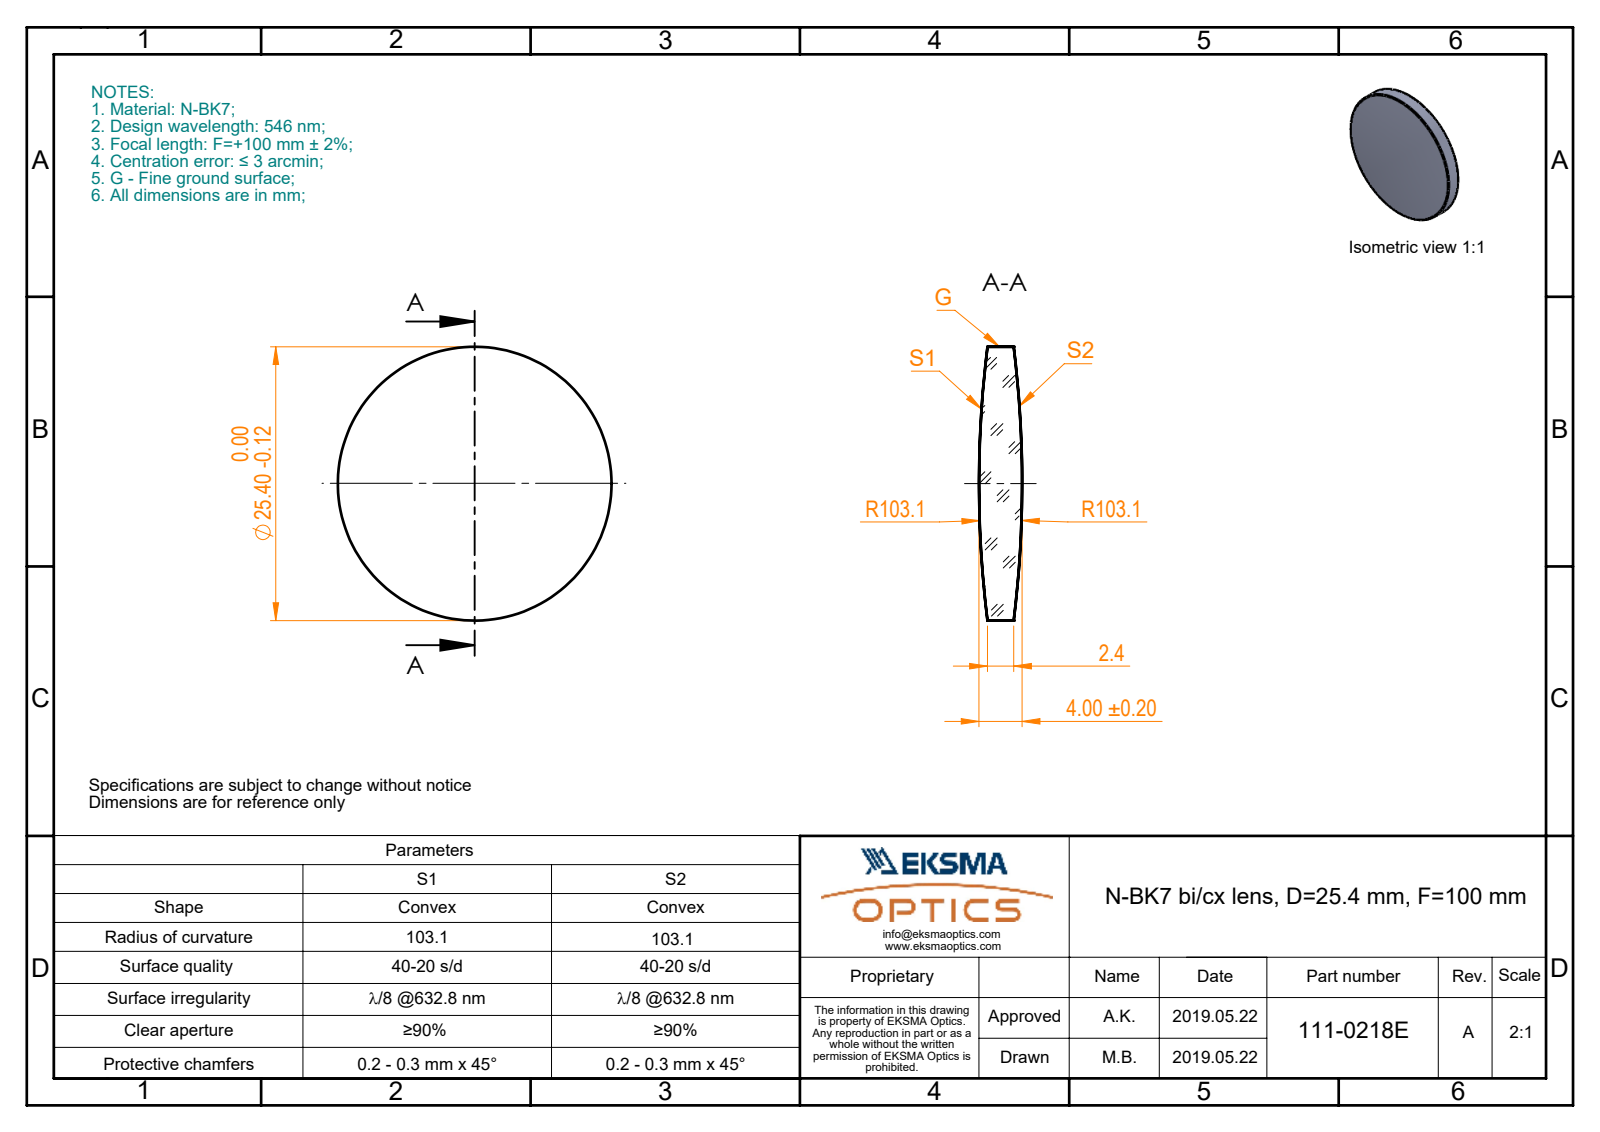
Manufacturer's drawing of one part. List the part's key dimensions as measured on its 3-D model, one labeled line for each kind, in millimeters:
Part name (STEP PRODUCT): 111-0218E BK7 bi-cx 25.4 F100
STEP written by: SolidWorks 2017 (CONFIG_CONTROL_DESIGN)
Units: millimetres
Bodies: 1 solid, 6 faces (0 planar, 2 cylindrical, 4 other)
Overall size (bounding box): 25.4 × 25.4 × 4
Volume: 1 629 mm³ · Surface area: 1 211 mm²
Round bosses / shafts (diameter × count): ⌀25.4 ×1
